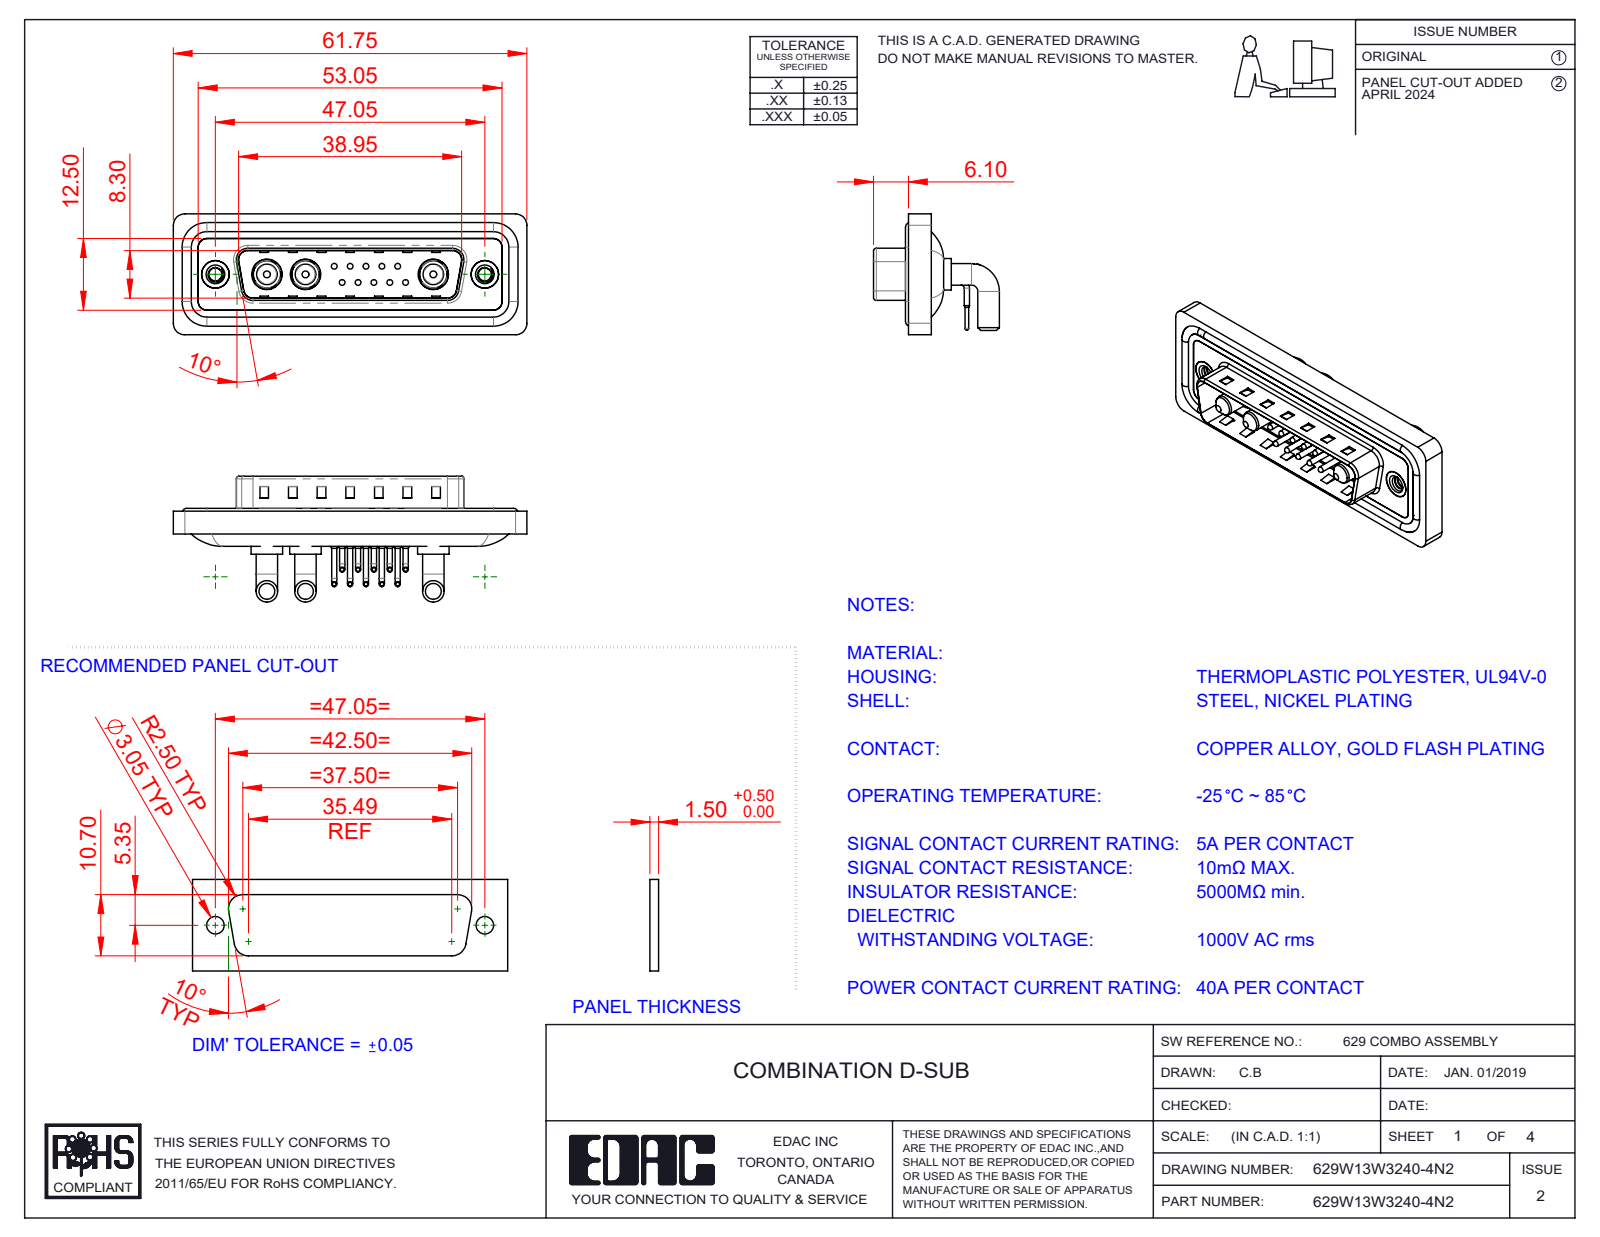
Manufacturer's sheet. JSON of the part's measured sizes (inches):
{"part_name": "629Combo Contact Row 2; 629Combo Shell Front_25 Contacts; 629Combo Shell Rear_25 Contacts; 629W13W3140-4N2 (+5 more)", "step_written_by": "SolidWorks 2023 (CONFIG_CONTROL_DESIGN)", "units": "inches", "bodies": {"solids": 23, "faces": 1712, "planar": 879, "cylindrical": 611, "other": 222}, "overall_size": [2.431, 0.865, 0.831], "volume_in3": 0.478, "surface_area_in2": 19.57, "round_holes": [[0.03, 10], [0.063, 10], [0.079, 10], [0.191, 3], [0.209, 3], [0.089, 2], [0.157, 2], [0.189, 2], [0.197, 2]], "round_bosses_or_shafts": [[0.035, 20], [0.059, 10], [0.039, 10], [0.026, 10], [0.148, 6], [0.063, 4], [0.217, 3], [0.205, 3]], "partial_cylinders_radius": [[0.059, 18], [0.079, 18], [0.04, 10], [0.02, 8], [0.063, 8], [0.01, 4], [0.024, 4], [0.026, 4]], "face_to_face_distances": [0.016, 0.114, 0.031, 0.161, 0.043, 0.083, 0.063, 0.177, 0.098, 0.059], "hole_center_spacings": [0.124, 0.109, 0.198, 0.218, 0.295, 0.198, 0.327, 0.398]}
